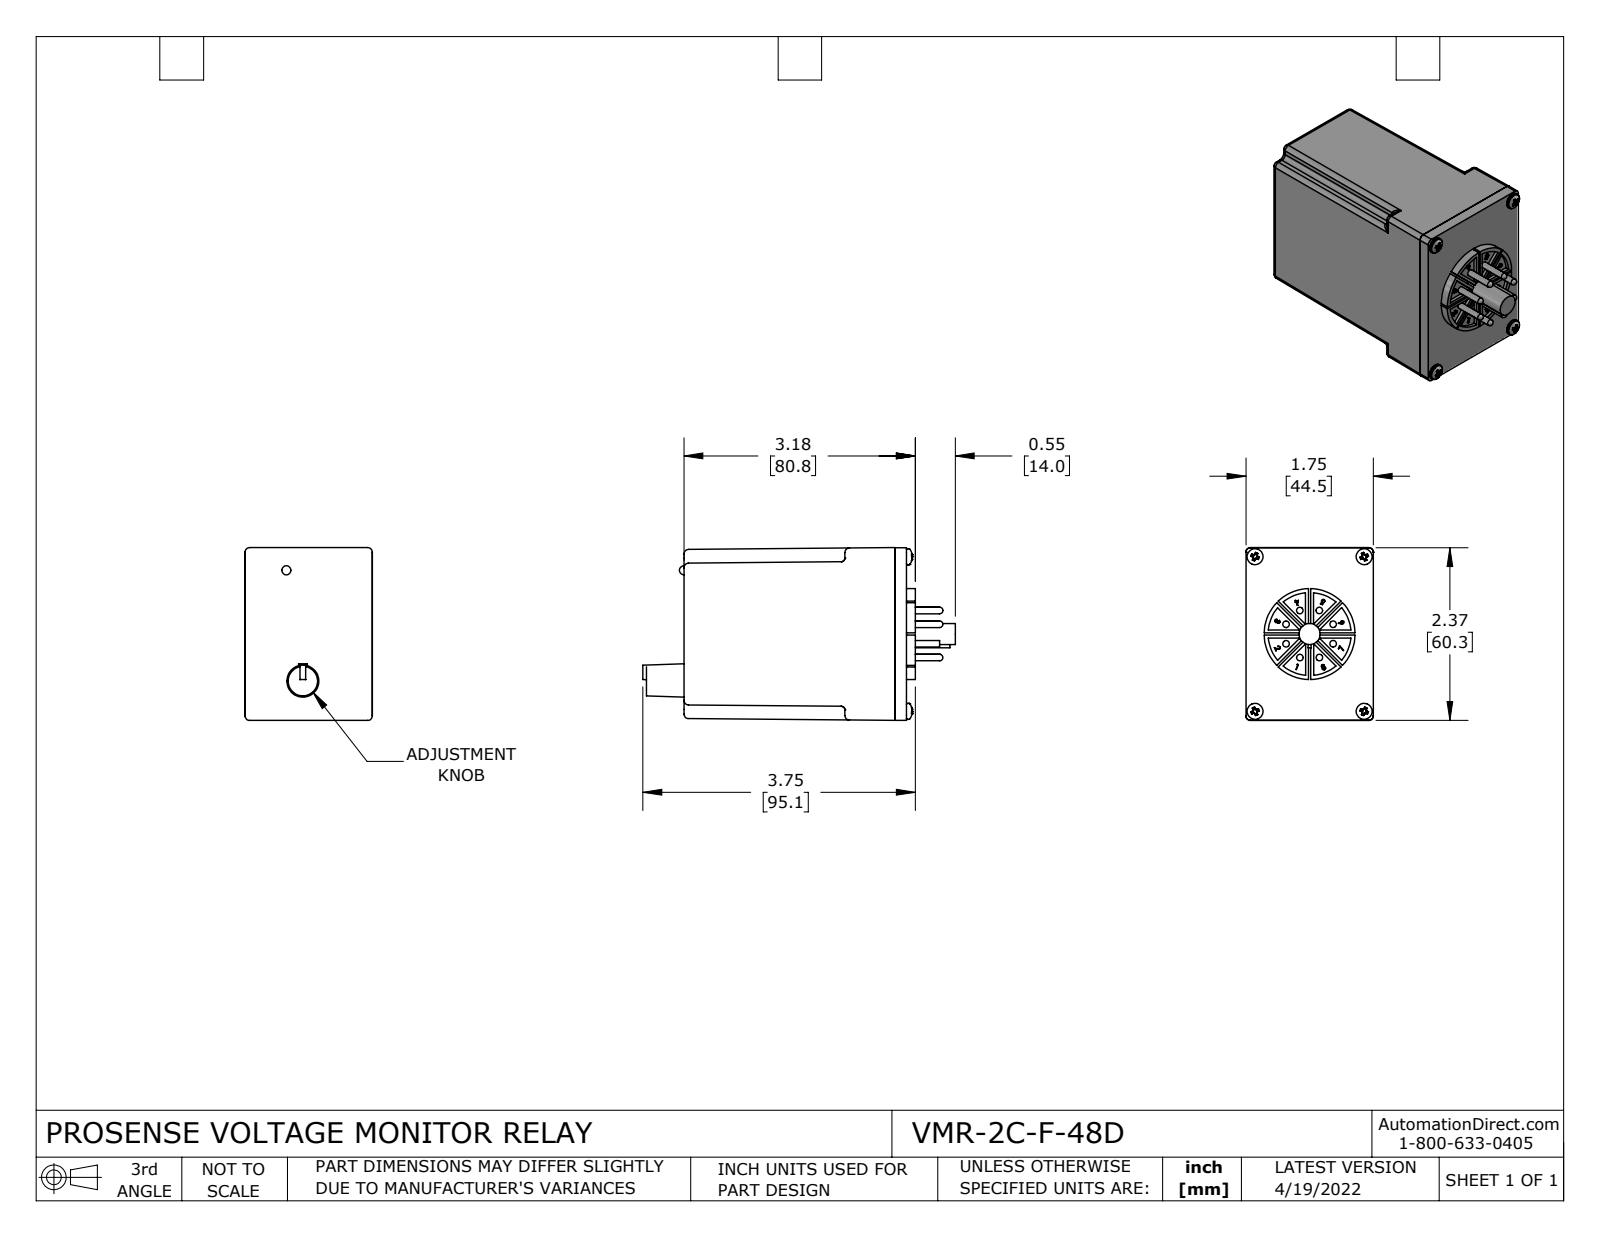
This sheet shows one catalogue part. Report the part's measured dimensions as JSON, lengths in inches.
{"part_name": "VMR-2C-F-48D", "step_written_by": "SolidWorks 2021 (CONFIG_CONTROL_DESIGN)", "units": "inches", "bodies": {"solids": 17, "faces": 542, "planar": 221, "cylindrical": 164, "other": 157}, "overall_size": [4.295, 2.375, 1.75], "volume_in3": 12.33, "surface_area_in2": 45.79, "round_holes": [[0.125, 4]], "round_bosses_or_shafts": [[0.09, 8], [0.219, 4], [1.25, 1], [0.29, 1]], "partial_cylinders_radius": [[0.063, 32], [0.005, 8], [0.05, 4], [0.57, 1]], "face_to_face_distances": [2.9, 0.16, 3.06, 0.07, 0.23, 3.13, 0.188, 0.05, 0.12, 0.28], "hole_center_spacings": [1.5, 2.125, 2.601]}
